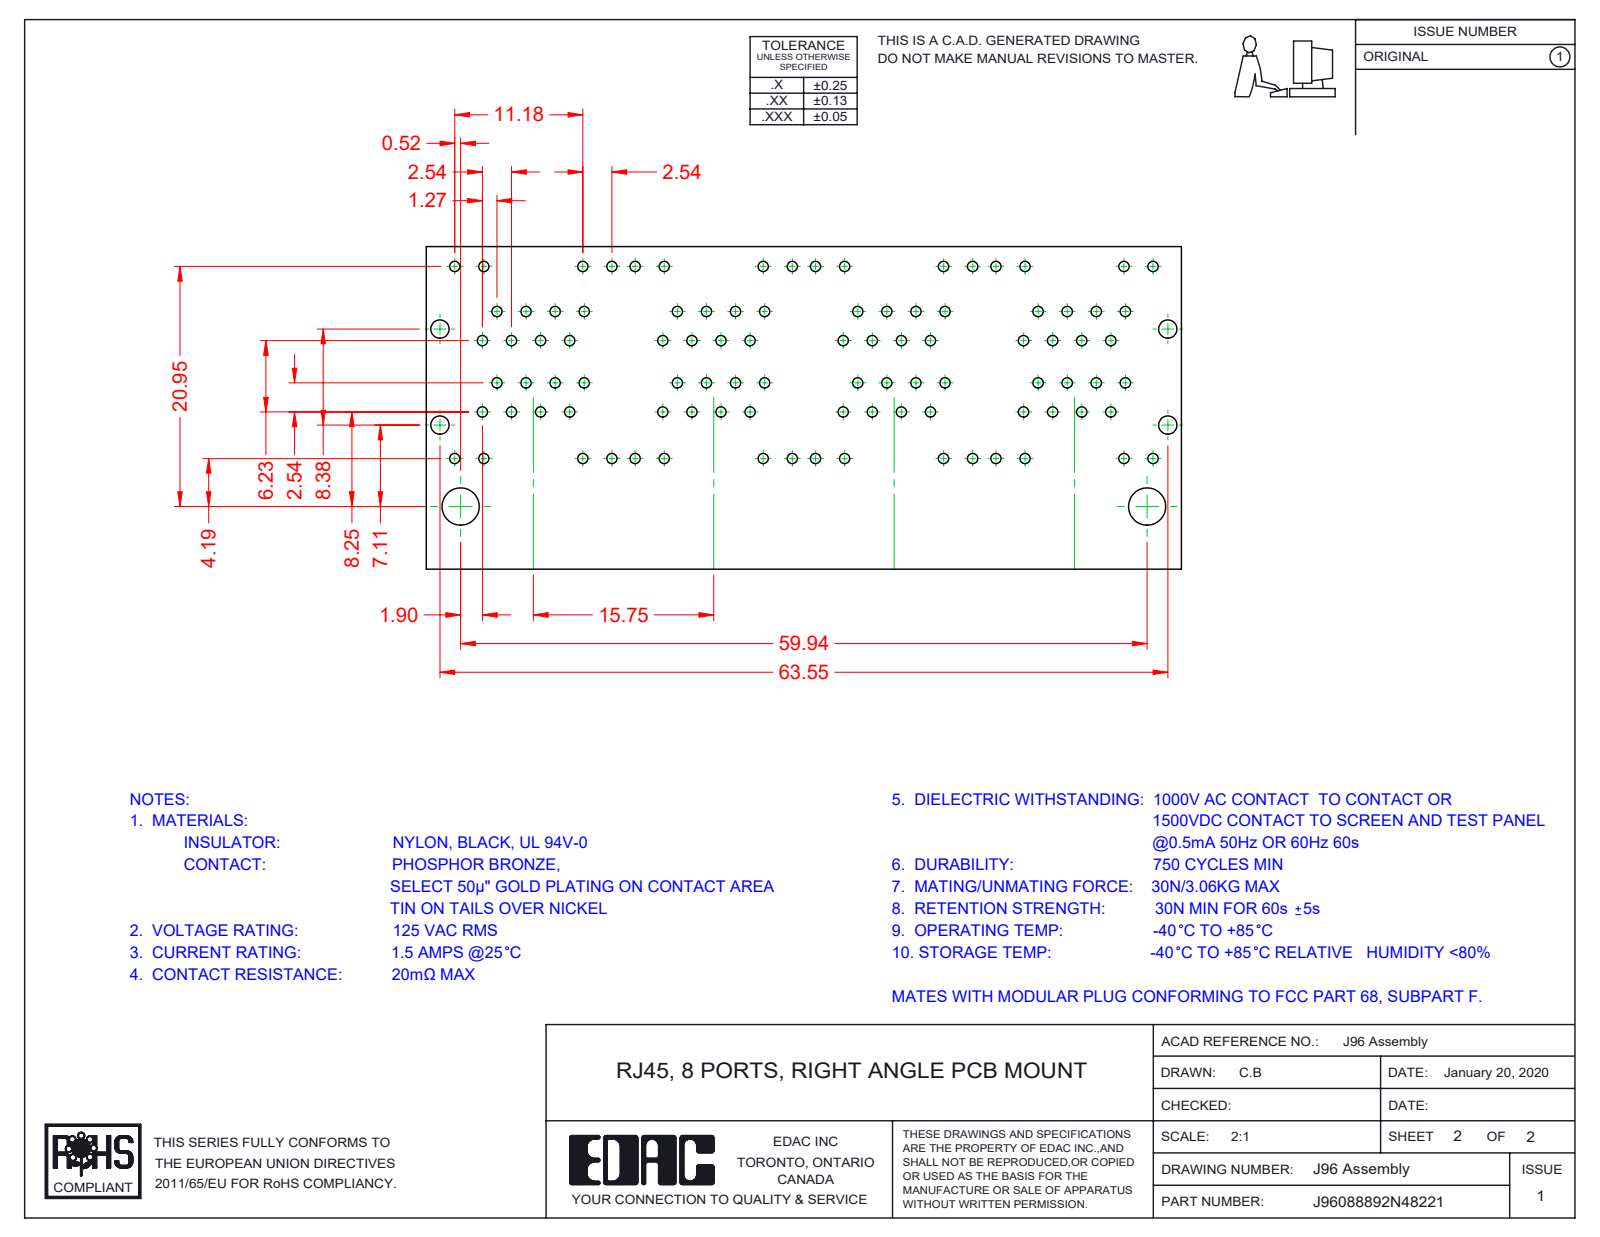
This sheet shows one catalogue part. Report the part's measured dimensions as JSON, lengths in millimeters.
{"part_name": "96 Contact Lock Lower; 96 Contacts Upper; 96 Shield_8 Ports LED - EMI; 96 Grounding_8 Ports (+8 more)", "step_written_by": "SolidWorks 2016 (CONFIG_CONTROL_DESIGN)", "units": "millimeters", "bodies": {"solids": 96, "faces": 7820, "planar": 6105, "cylindrical": 1404, "other": 311}, "overall_size": [67.35, 31.38, 28.68], "volume_mm3": 24149, "surface_area_mm2": 63596, "round_holes": [[1.7, 3]], "round_bosses_or_shafts": [[1.68, 3]], "partial_cylinders_radius": [[0.25, 124], [0.35, 73], [1, 72], [0.5, 49], [0.91, 32], [0.2, 27], [0.27, 14], [0.7, 11]], "face_to_face_distances": [15.75, 0.35, 9.95, 1.17, 1.6, 0.54, 9.98, 10.18, 12.67, 3.37], "hole_center_spacings": [15.75, 31.5]}
